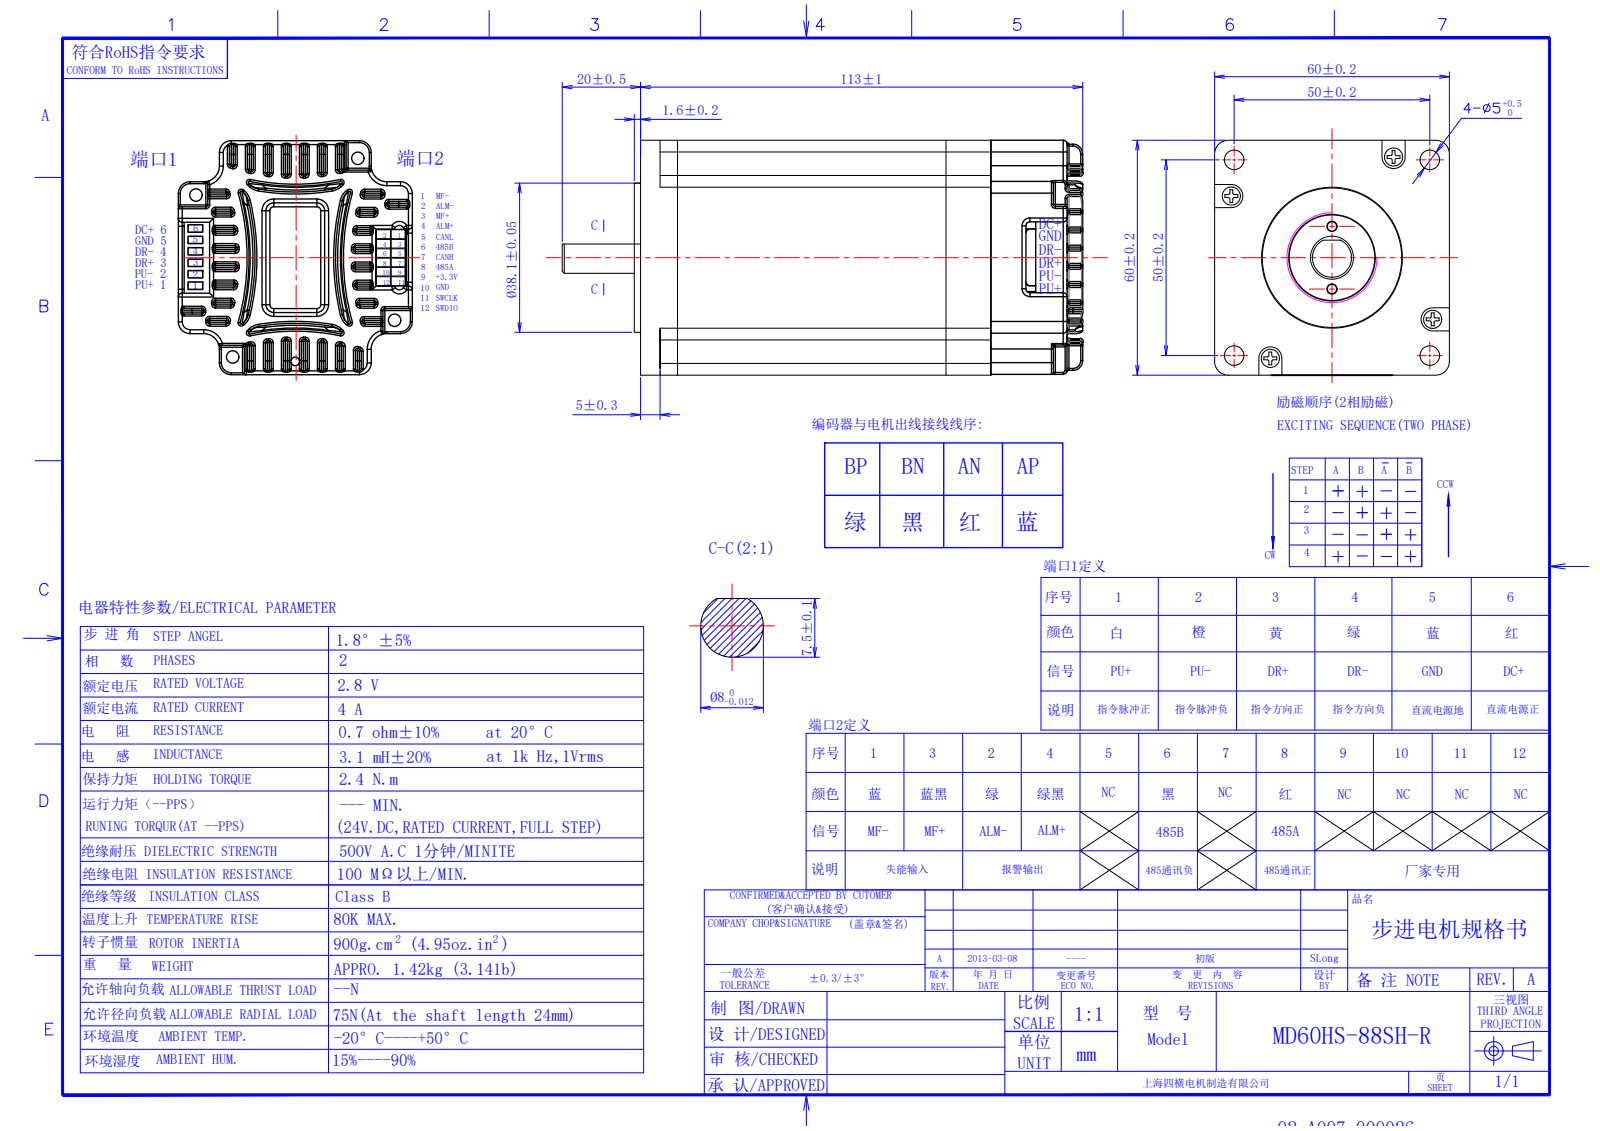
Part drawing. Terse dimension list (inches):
name: 01.B013.000062 60BH新款编码器后罩; 60前端盖; 60定子66.5; M3螺钉-L82 (+7 more)
written by: SolidWorks 2022 (CONFIG_CONTROL_DESIGN)
unit: in
bodies: 16 solids, 2592 faces (1055 planar, 857 cylindrical, 680 other)
size: 5.177 × 2.362 × 2.362
volume: 18.87 in³; area: 117.1 in²
holes: 7× ⌀0.197, 4× ⌀0.079, 4× ⌀0.081, 4× ⌀0.098, 4× ⌀0.122, 4× ⌀0.13, 2× ⌀0.043, 1× ⌀0.055, 1× ⌀0.087, 1× ⌀0.394, 1× ⌀0.413
bosses: 8× ⌀0.118, 6× ⌀0.024, 4× ⌀0.217, 4× ⌀0.197, 2× ⌀0.083, 1× ⌀1.5
rounds: 294× R0.02, 46× R0.039, 42× R0.079, 33× R0.118, 19× R0.012, 12× R0.157, 8× R0.016, 8× R0.017
face distances: 2.618, 2.362, 0.063, 0.413, 3.807, 0.433, 3.051, 0.343, 0.776, 3.394
hole spacings: 1.616, 1.74, 2.074, 0.023, 0.344, 0.361, 0.362, 0.594
